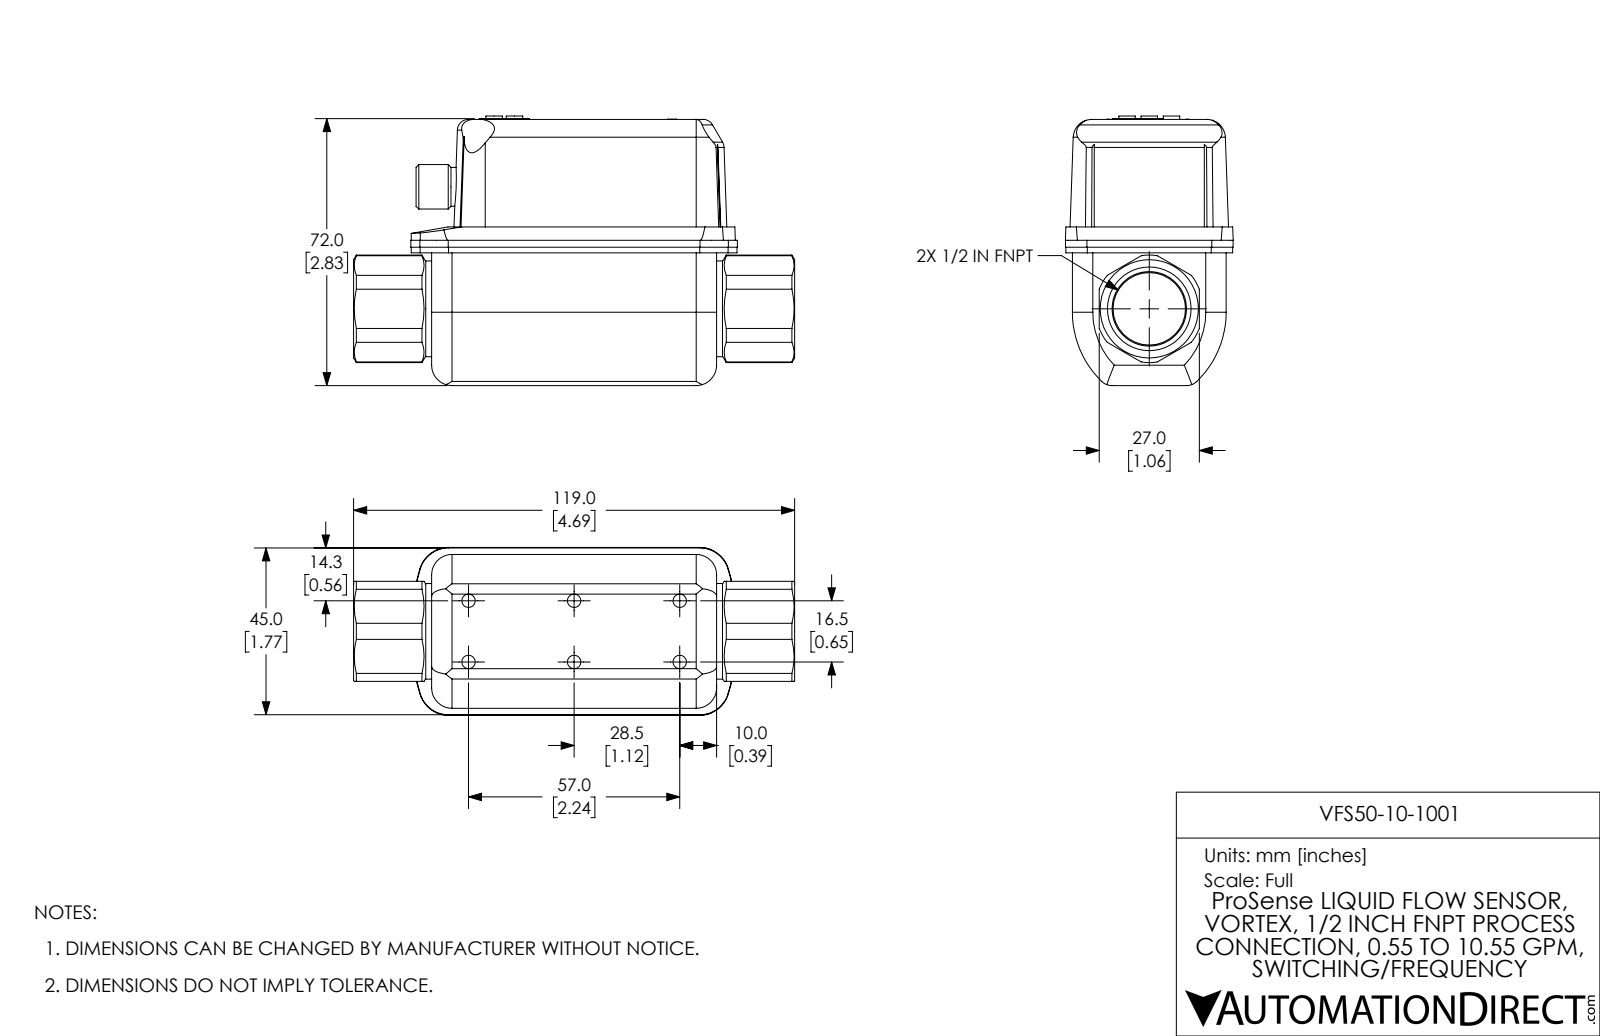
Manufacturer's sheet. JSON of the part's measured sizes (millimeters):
{"part_name": "VFS50-10-1001", "step_written_by": "SolidWorks 2017 (AUTOMOTIVE_DESIGN)", "units": "millimeters", "bodies": {"solids": 1, "faces": 219, "planar": 84, "cylindrical": 80, "other": 55}, "overall_size": [119, 72.7, 45.29], "volume_mm3": 234166, "surface_area_mm2": 27599, "round_holes": [[3.6, 6], [8.4, 1]], "round_bosses_or_shafts": [[4.45, 3], [25.8, 1], [12, 1], [10.5, 1]], "partial_cylinders_radius": [[8, 12], [5.5, 6], [4, 4], [60, 4], [3.5, 2], [5, 2], [26, 2], [0.6, 1]], "face_to_face_distances": [27, 71.8, 41.5, 36, 7.25, 34.25, 71.75, 35.8, 35.95, 11.05], "hole_center_spacings": [28.5, 32.93, 16.5, 57, 59.34]}
